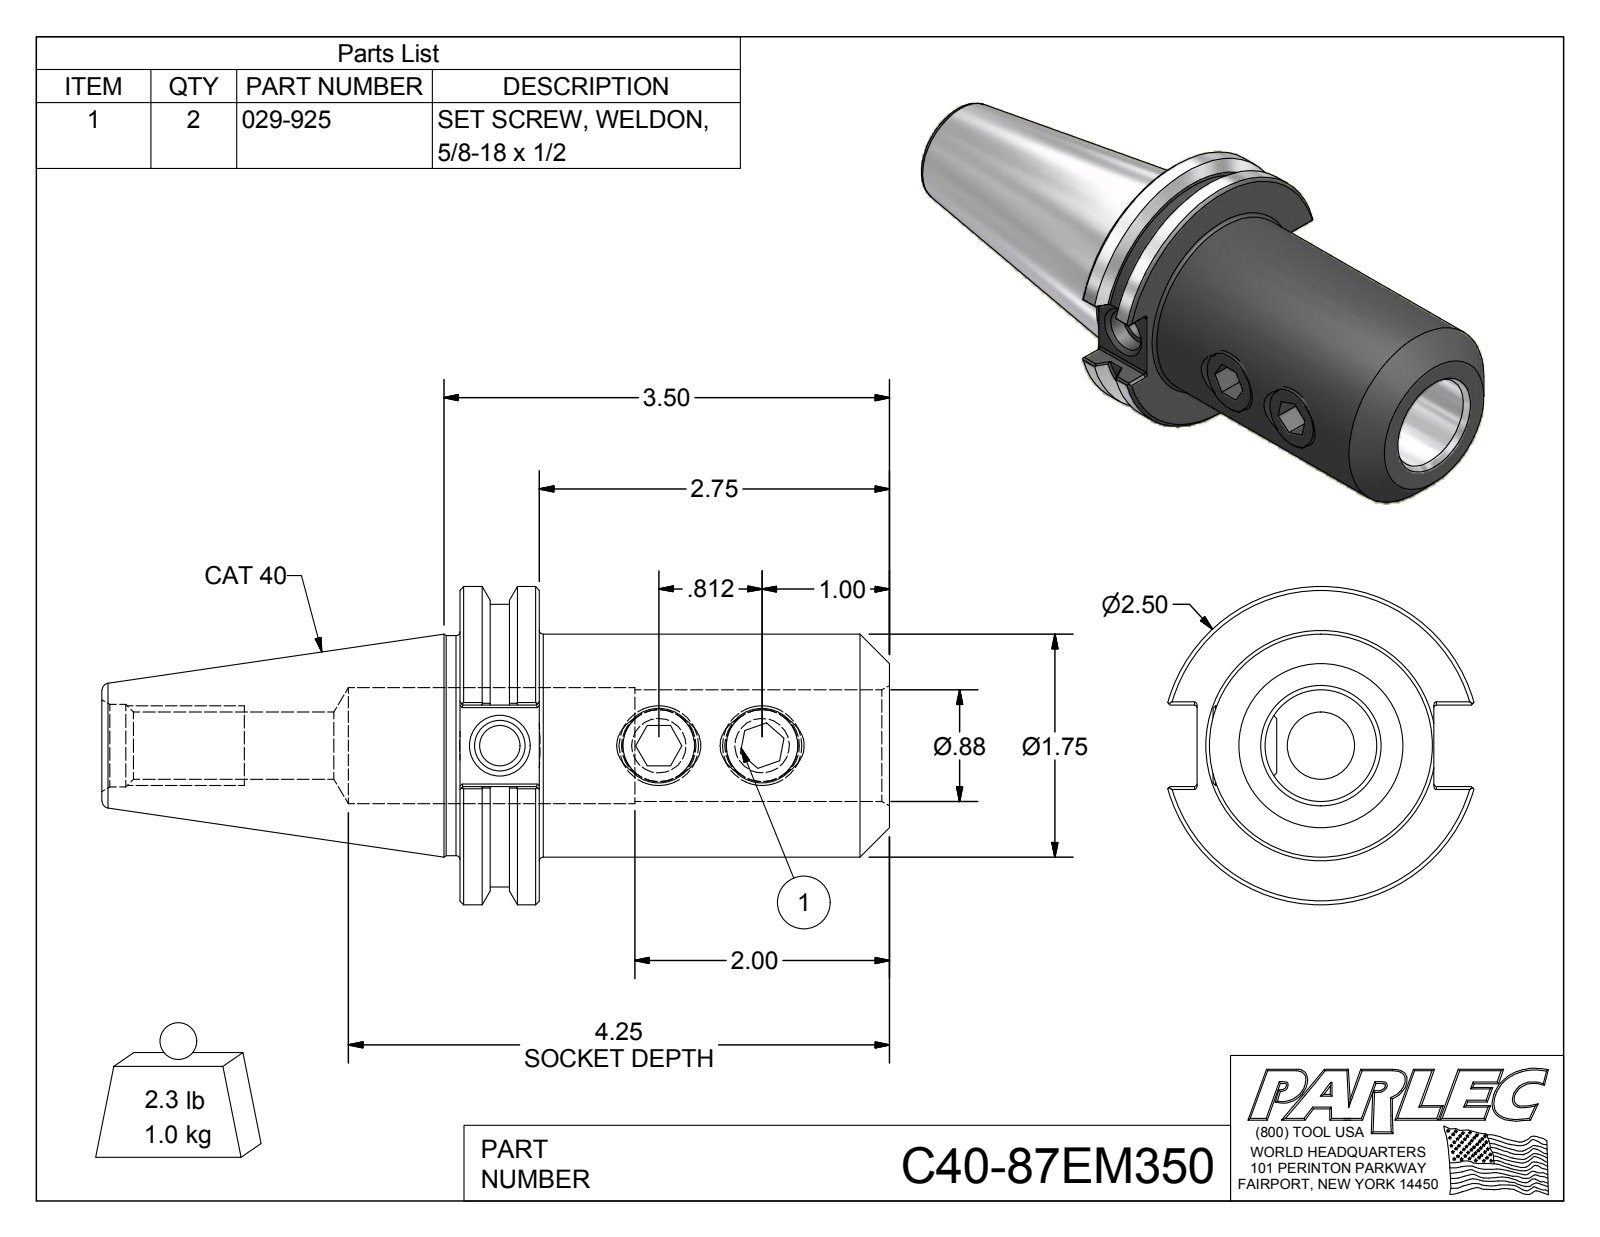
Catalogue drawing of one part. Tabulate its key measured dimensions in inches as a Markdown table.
| quantity | value |
| --- | --- |
| part name | C40-87EM350; C40-87EM350-1; 029-925 |
| STEP written by | Autodesk Inventor 2012 (AUTOMOTIVE_DESIGN) |
| units | inches |
| bodies | 3 solids, 116 faces (50 planar, 30 cylindrical, 36 other) |
| overall size | 6.187 × 2.5 × 2.406 |
| volume | 10.24 in³ |
| surface area | 59.2 in² |
| round holes (diameter × count) | 0.565 × 2, 0.315 × 1, 0.399 × 1, 0.527 × 1, 0.648 × 1, 0.875 × 1, 0.91 × 1 |
| round bosses / shafts (diameter × count) | 0.625 × 2, 2.5 × 1, 2.219 × 1, 1.75 × 1, 1.73 × 1 |
| partial cylindrical surfaces (radius × count) | 0.02 × 12 |
| main face-to-face distances | 0.625, 3.375, 2.75, 0.315, 1.735, 1.235, 0.5, 0.64, 1.86, 0.626 |
| hole center spacings | 0.812, 1.248, 2.06 |
